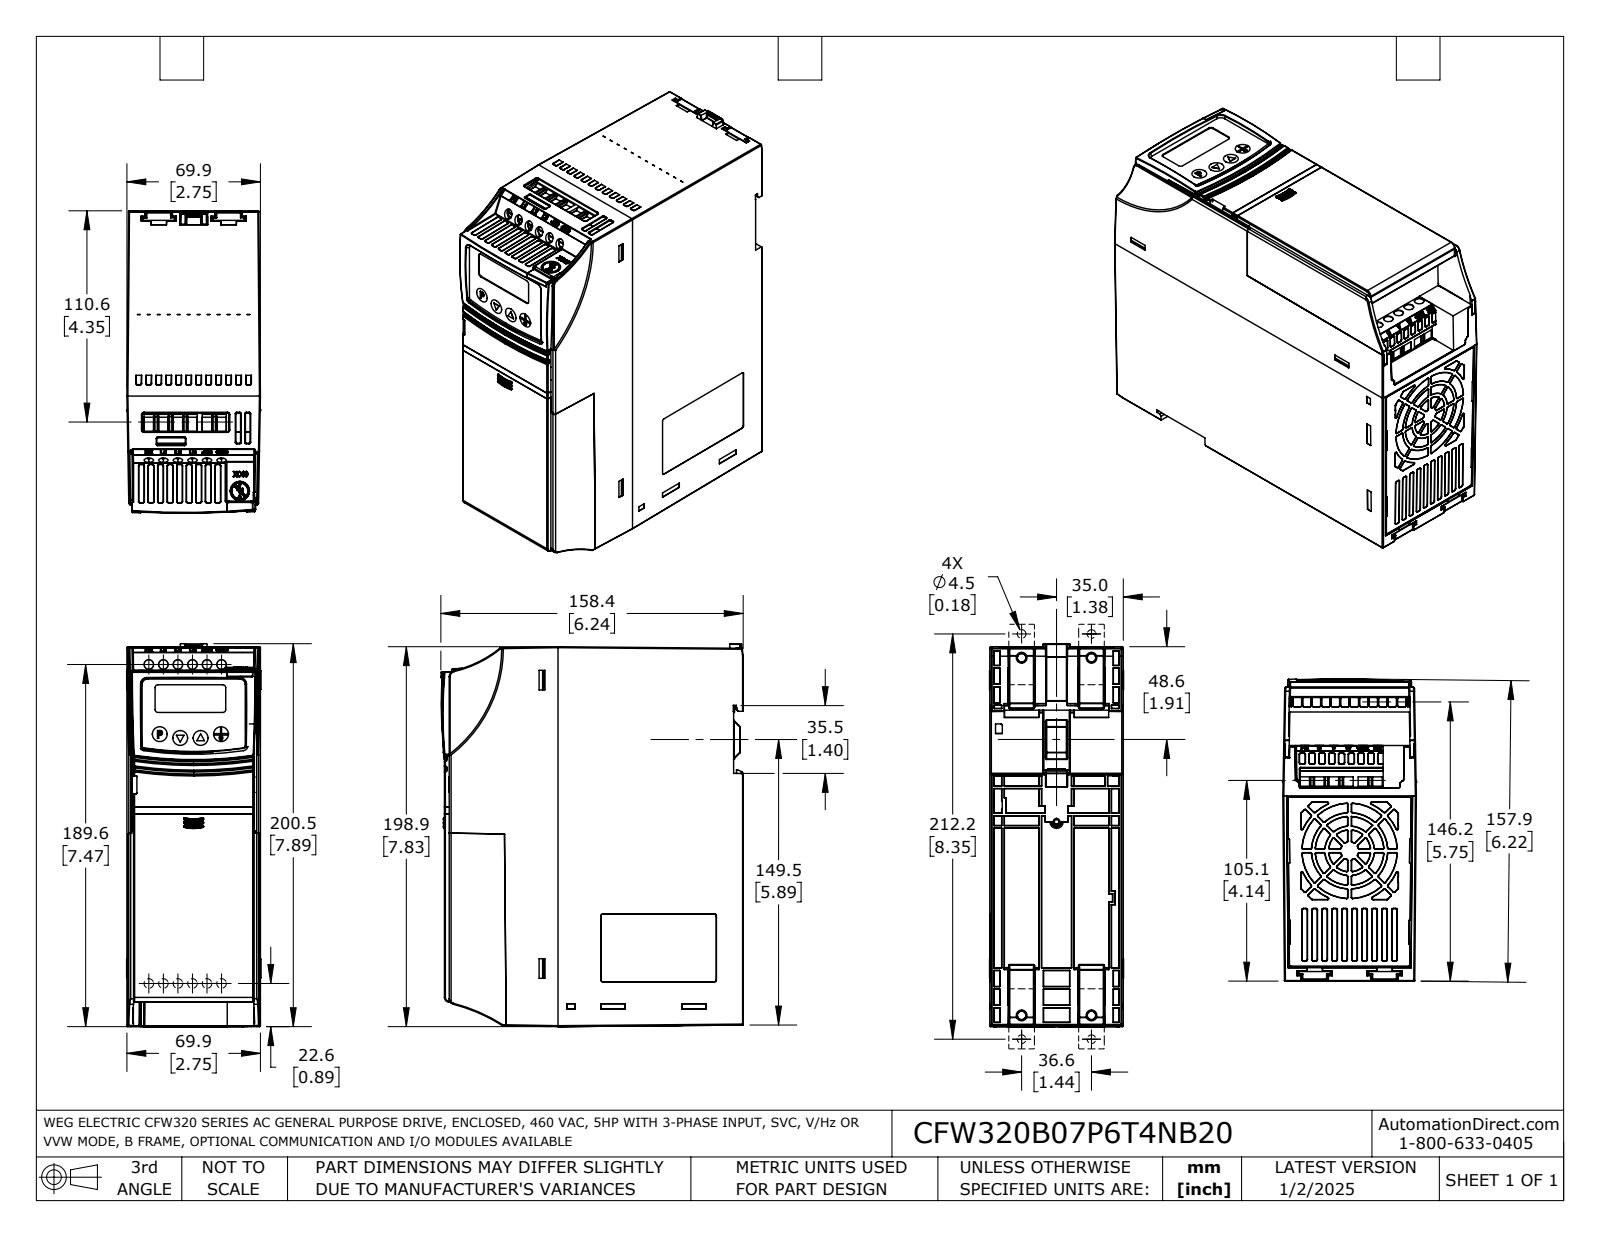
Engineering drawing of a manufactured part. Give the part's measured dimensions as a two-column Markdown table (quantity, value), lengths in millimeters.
| quantity | value |
| --- | --- |
| part name | CFW320B07P6T4NB20 |
| STEP written by | SolidWorks 2021 (AUTOMOTIVE_DESIGN) |
| units | millimeters |
| bodies | 5 solids, 3984 faces (1907 planar, 899 cylindrical, 1178 other) |
| overall size | 200.5 × 158.4 × 70.2 |
| volume | 401 600 mm³ |
| surface area | 248 500 mm² |
| round holes (diameter × count) | 4.9 × 6 |
| partial cylindrical surfaces (radius × count) | 0.3 × 355, 0.5 × 181, 1 × 14, 0.8 × 7, 3 × 5, 0.3 × 2, 2.8 × 2, 2.5 × 1 |
| main face-to-face distances | 5.3, 2.5, 2.5, 148, 145.5, 5.4, 150.9, 153.3, 190.5, 1 |
| hole center spacings | 7.6, 15.2, 22.9, 30.5, 38.1 |
